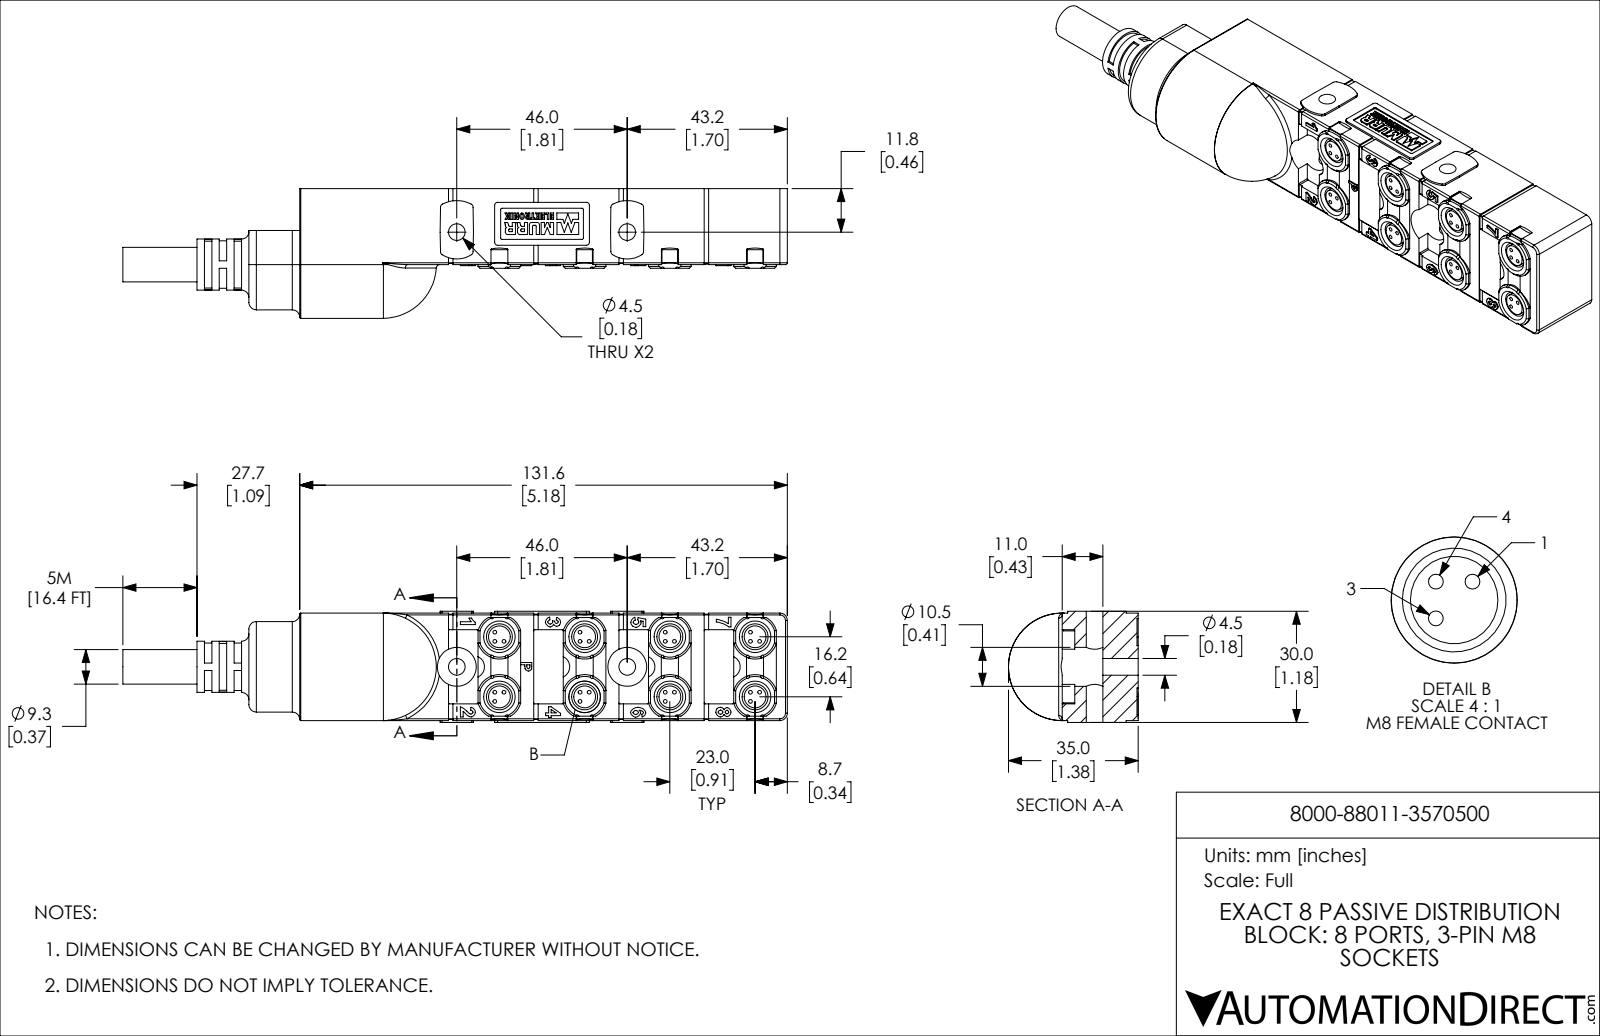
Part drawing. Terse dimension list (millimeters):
name: 8000-88011-3570500
written by: SolidWorks 2019 (CONFIG_CONTROL_DESIGN)
unit: mm
bodies: 1 solid, 1306 faces (678 planar, 429 cylindrical, 199 other)
size: 179.3 × 35 × 30
volume: 94 670 mm³; area: 21 030 mm²
holes: 24× ⌀1, 8× ⌀7, 4× ⌀4.5, 2× ⌀10.5
bosses: 8× ⌀5.9, 2× ⌀11.4, 1× ⌀13.8, 1× ⌀12.8, 1× ⌀9.3
rounds: 35× R0.5, 24× R0.2, 18× R0.3, 12× R10, 8× R1, 8× R6, 6× R2, 4× R0.3
face distances: 29, 20.5, 0.5, 29.5, 20.2, 11, 11.3, 9.2, 30, 9.5
hole spacings: 1.8, 23, 15, 46, 2.5, 16.2, 24.3, 26.4
